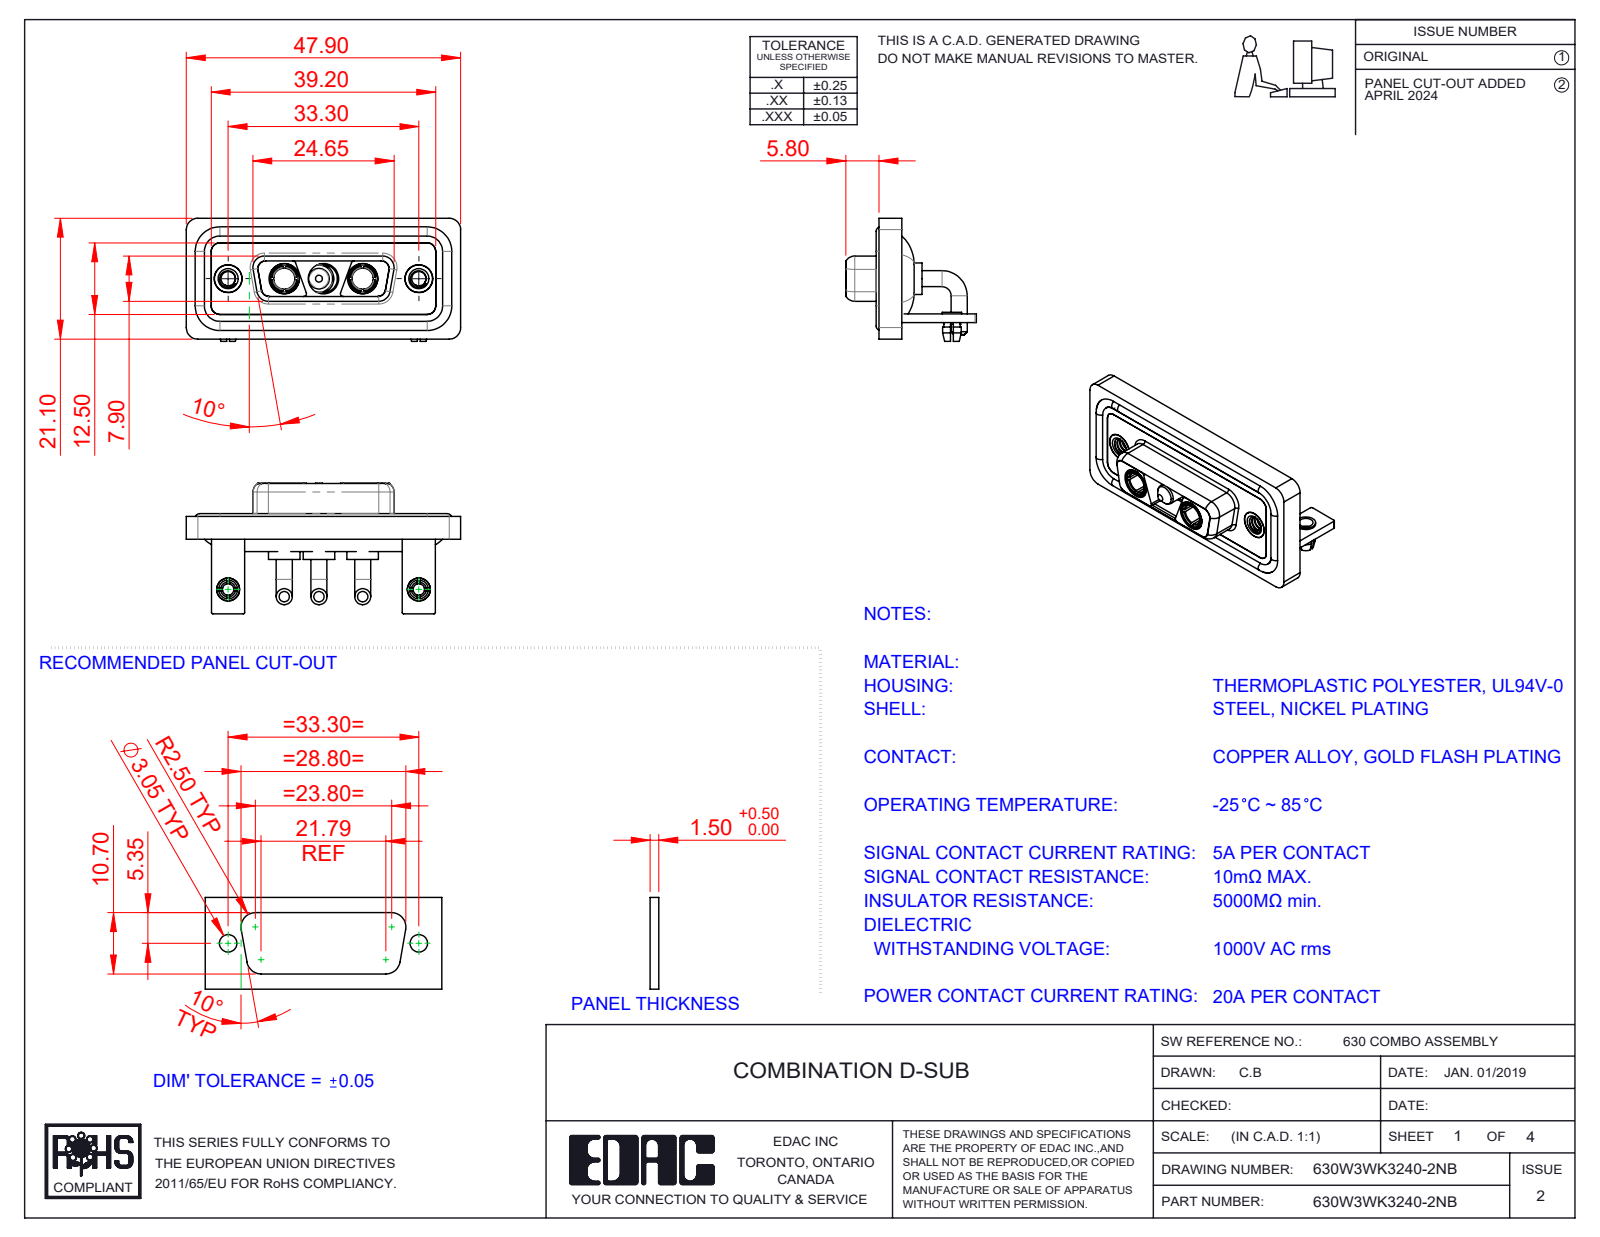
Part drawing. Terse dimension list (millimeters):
name: 630Combo Housing_3WK3; 630Combo Board Lock_50 Contacts; Power Socket_20A RA; Power Pin_20A RA (+6 more)
written by: SolidWorks 2023 (CONFIG_CONTROL_DESIGN)
unit: mm
bodies: 17 solids, 729 faces (246 planar, 318 cylindrical, 165 other)
size: 47.9 × 22.8 × 21.5
volume: 6 427 mm³; area: 10 687 mm²
holes: 5× ⌀4.85, 4× ⌀2.5, 3× ⌀5.3, 2× ⌀2, 2× ⌀3.2, 2× ⌀3.7, 2× ⌀4, 2× ⌀4.05, 2× ⌀5
bosses: 6× ⌀2.8, 4× ⌀1.6, 3× ⌀5.5, 3× ⌀5.2, 3× ⌀4.75, 3× ⌀3.75, 2× ⌀4.96, 2× ⌀4.95
rounds: 21× R2, 18× R1.5, 16× R0.25, 12× R1.35, 9× R0.5, 8× R1.6, 4× R0.6, 4× R0.65
face distances: 0.4, 2.9, 1.5, 3.7, 1.8, 1.1, 4.1, 1.6, 2.5, 1.4
hole spacings: 6.85, 9.8, 16.65, 23.5, 33.3, 13.7
